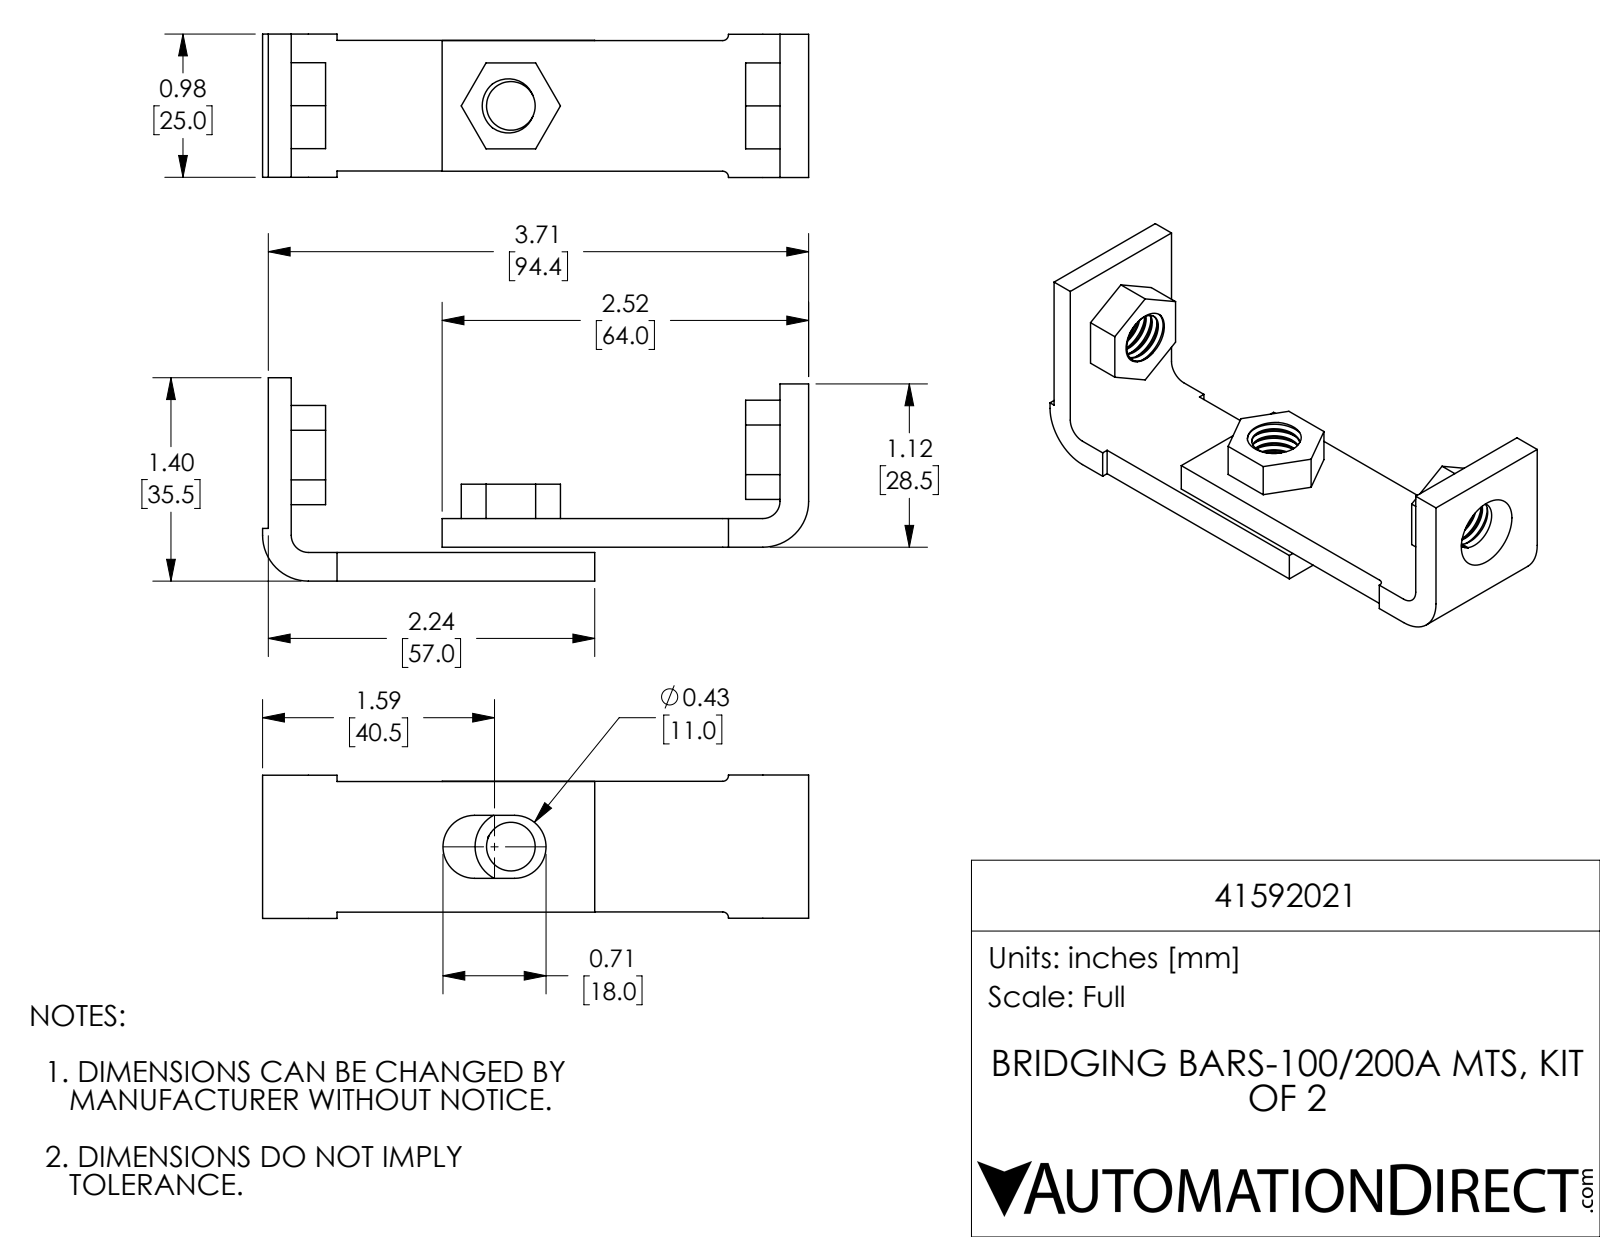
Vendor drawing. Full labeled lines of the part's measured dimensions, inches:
Part name (STEP PRODUCT): 41592021
STEP written by: SolidWorks 2017 (AUTOMOTIVE_DESIGN)
Units: inches
Bodies: 5 solids, 154 faces (58 planar, 90 cylindrical, 6 other)
Overall size (bounding box): 3.754 × 1.398 × 0.986
Volume: 1.208 in³ · Surface area: 20.25 in²
Round holes (diameter × count): ⌀0.335 ×3, ⌀0.394 ×3, ⌀0.492 ×3
Round bosses / shafts (diameter × count): ⌀0.512 ×3
Partial cylindrical surfaces — rounded edges, fillets, slot ends (radius × count): R0.039 ×2, R0.118 ×2, R0.217 ×2, R0.315 ×2
Main face-to-face distances: 0.197, 0.233, 0.43, 0.036, 0.043, 0.941, 0.157, 3.518, 0.898, 0.591
Hole centre spacings: 0.036
